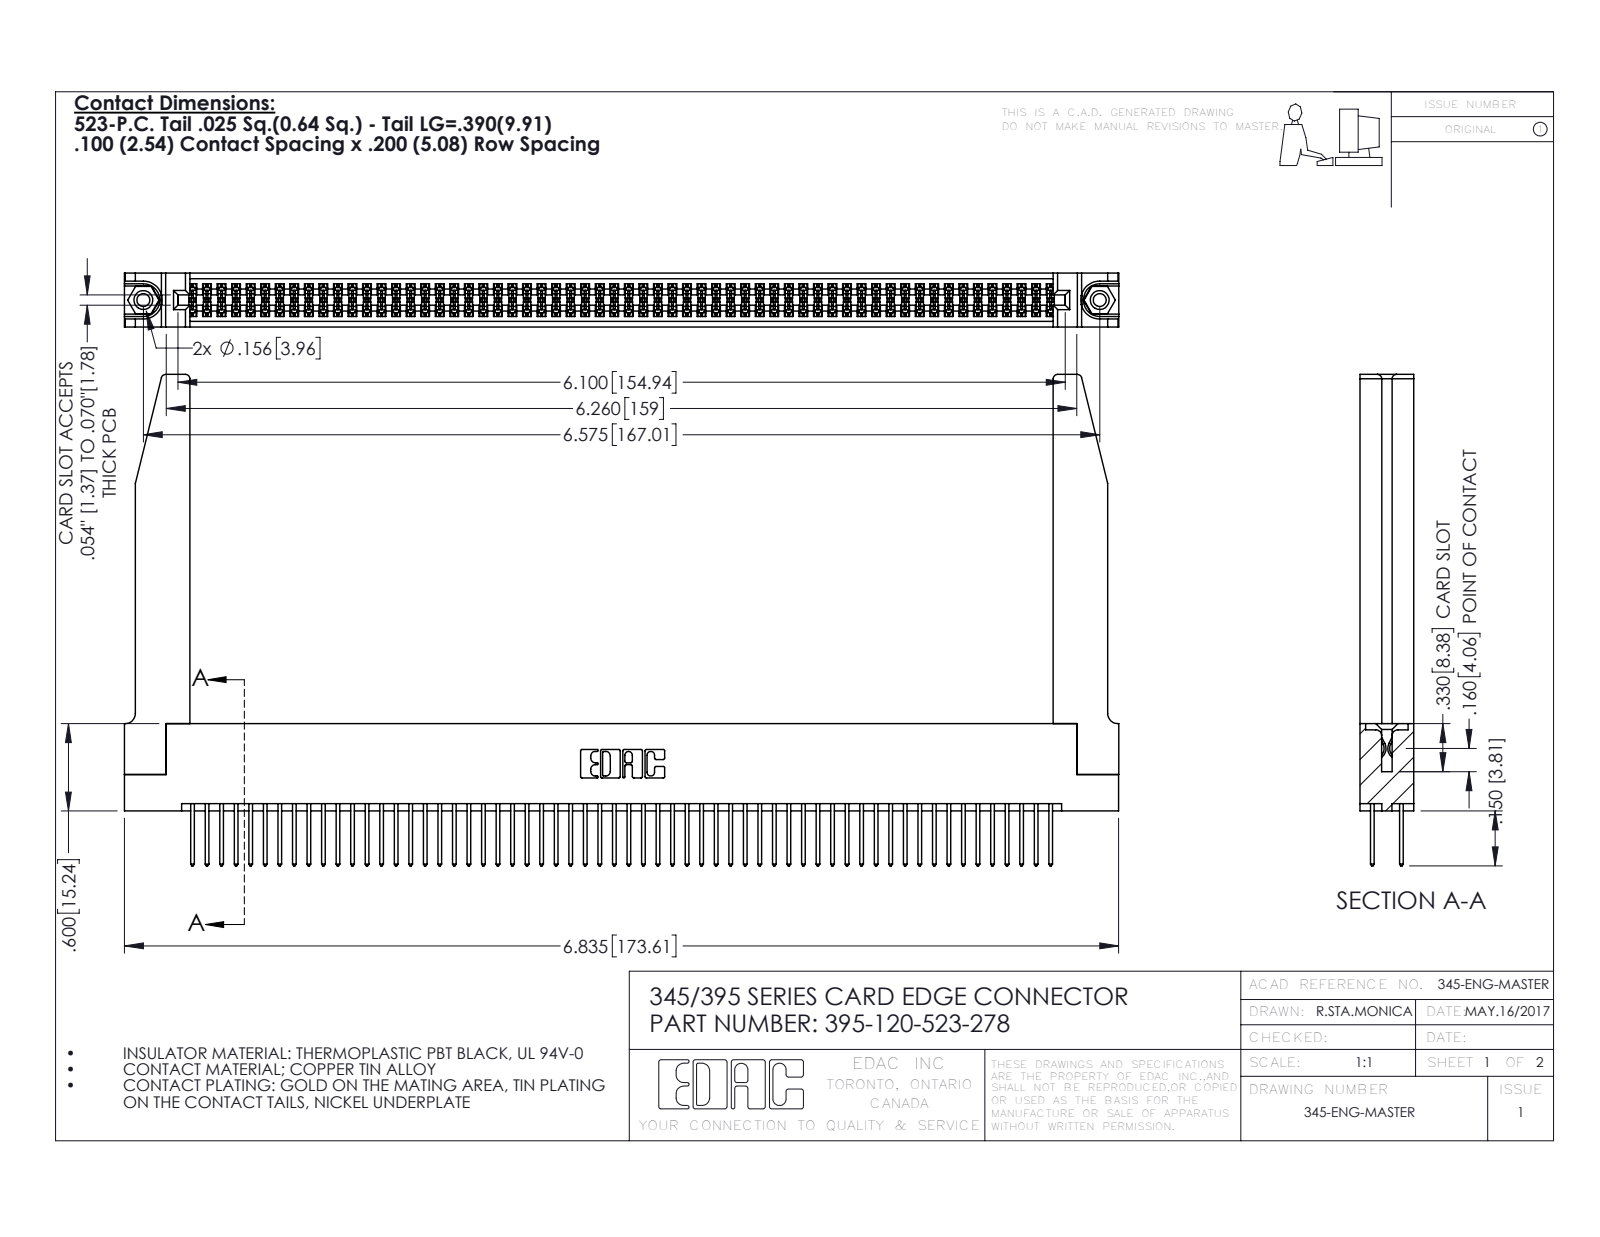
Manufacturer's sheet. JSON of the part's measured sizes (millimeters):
{"part_name": "345-292-001_345-293-123; 345-220-078_345-220-078; 395-120-523-278; 345-250-001_345-250-001-102 (+1 more)", "step_written_by": "SolidWorks 2016 (CONFIG_CONTROL_DESIGN)", "units": "millimeters", "bodies": {"solids": 125, "faces": 6360, "planar": 4182, "cylindrical": 2126, "other": 52}, "overall_size": [173.6, 85.8, 9.4], "volume_mm3": 25060, "surface_area_mm2": 33830, "round_holes": [[2.3, 2], [3.2, 2], [4, 2], [1.6, 1]], "round_bosses_or_shafts": [[3.9, 2]], "partial_cylinders_radius": [[0.2, 180], [0.3, 120], [0.3, 22], [0.8, 8], [0.2, 6], [0.8, 6], [0.7, 3], [0.4, 2]], "face_to_face_distances": [1.8, 7.6, 9.4, 5.1, 2.5, 6.9, 0.6, 5.7, 4.4, 3.8], "hole_center_spacings": [6.9, 161, 167]}
